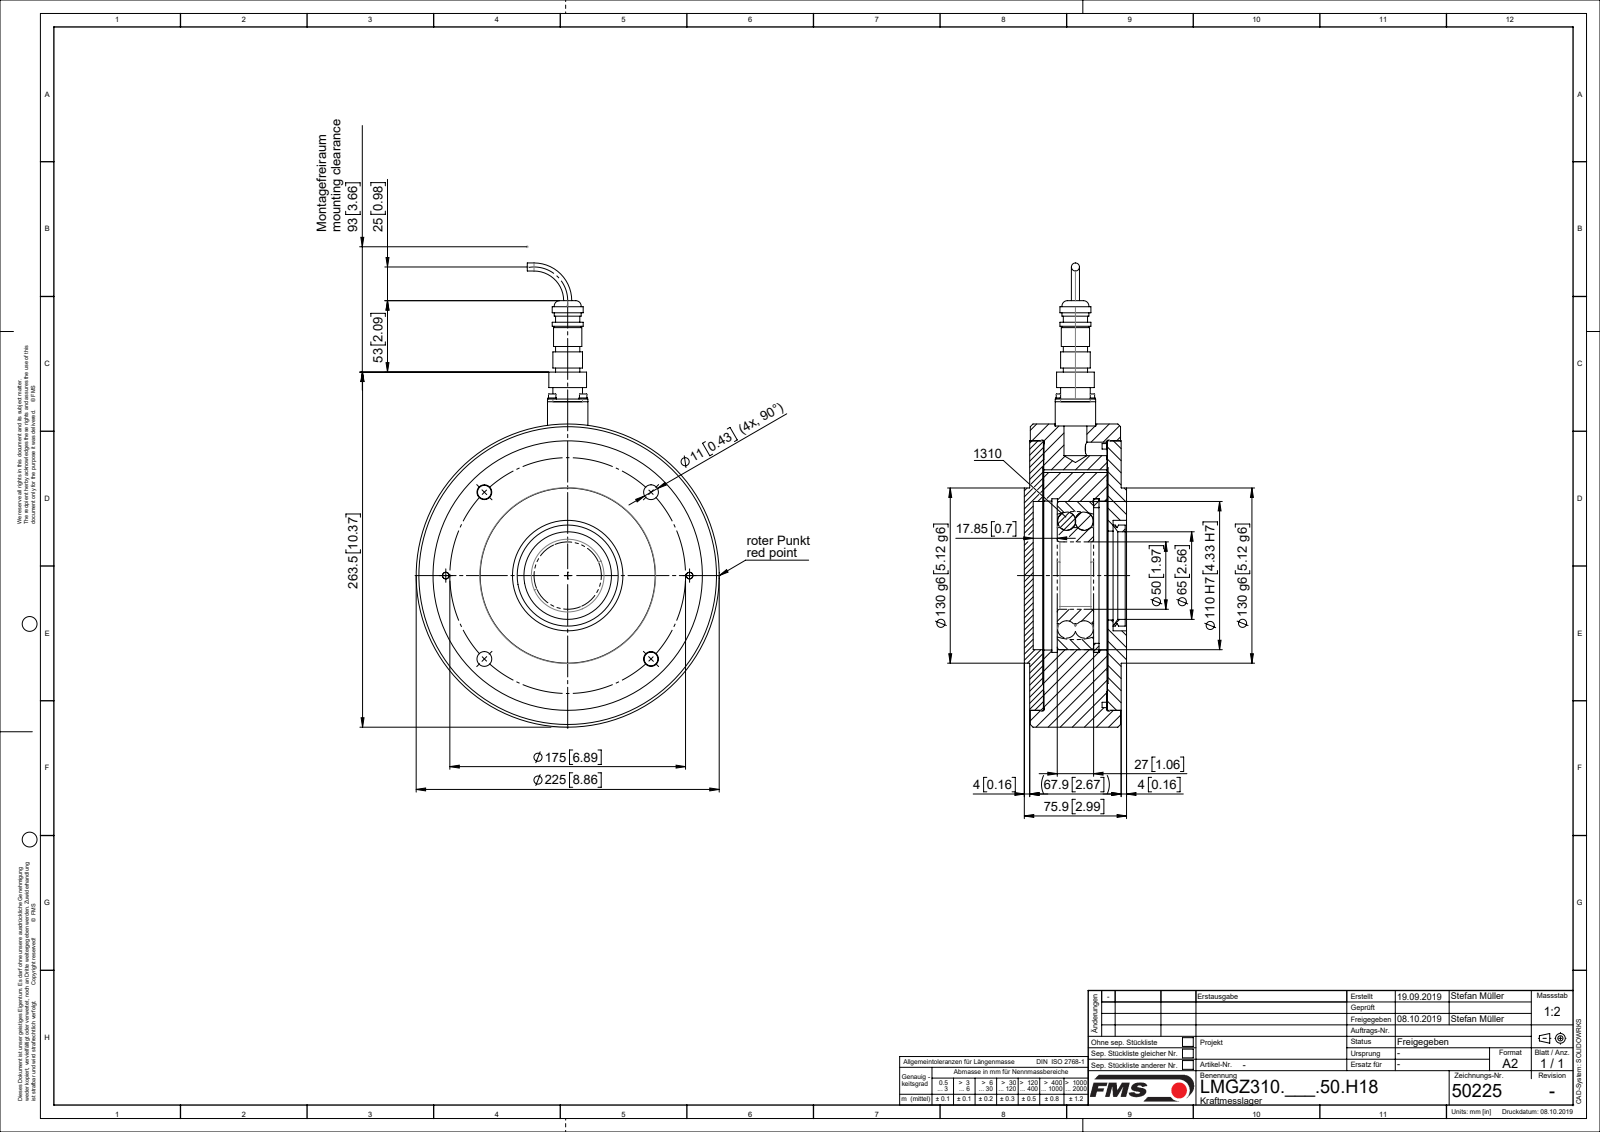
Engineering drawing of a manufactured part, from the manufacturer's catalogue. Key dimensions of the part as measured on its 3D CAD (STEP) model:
Part name (STEP PRODUCT): L50225; L4765504; TEIL1; L49152 (+8 more)
STEP written by: Mechanical Desktop 2007 (CONFIG_CONTROL_DESIGN)
Units: millimetres
Bodies: 20 solids, 389 faces (99 planar, 232 cylindrical, 58 other)
Overall size (bounding box): 344.5 × 225 × 75.9
Volume: 2 413 000 mm³ · Surface area: 392 027 mm²
Round holes (diameter × count): ⌀11 ×6, ⌀2.6 ×4, ⌀3.2 ×4, ⌀3.4 ×4, ⌀9 ×4, ⌀5 ×2, ⌀6.6 ×2, ⌀50 ×1, ⌀64 ×1, ⌀66 ×1, ⌀82 ×1, ⌀88.2 ×1
Round bosses / shafts (diameter × count): ⌀6.2 ×4, ⌀5.5 ×4, ⌀3 ×4, ⌀2.5 ×4, ⌀6 ×3, ⌀10 ×2, ⌀225 ×1, ⌀199 ×1
Partial cylindrical surfaces — rounded edges, fillets, slot ends (radius × count): R4 ×4, R81 ×1, R86 ×1
Main face-to-face distances: 9.7, 47.25, 10.45, 10.75, 47.45, 57.7, 10.2, 57.45, 47, 10
Hole centre spacings: 23, 68.17, 87.5, 123.74, 164.45, 32.53, 90.5, 174.99
